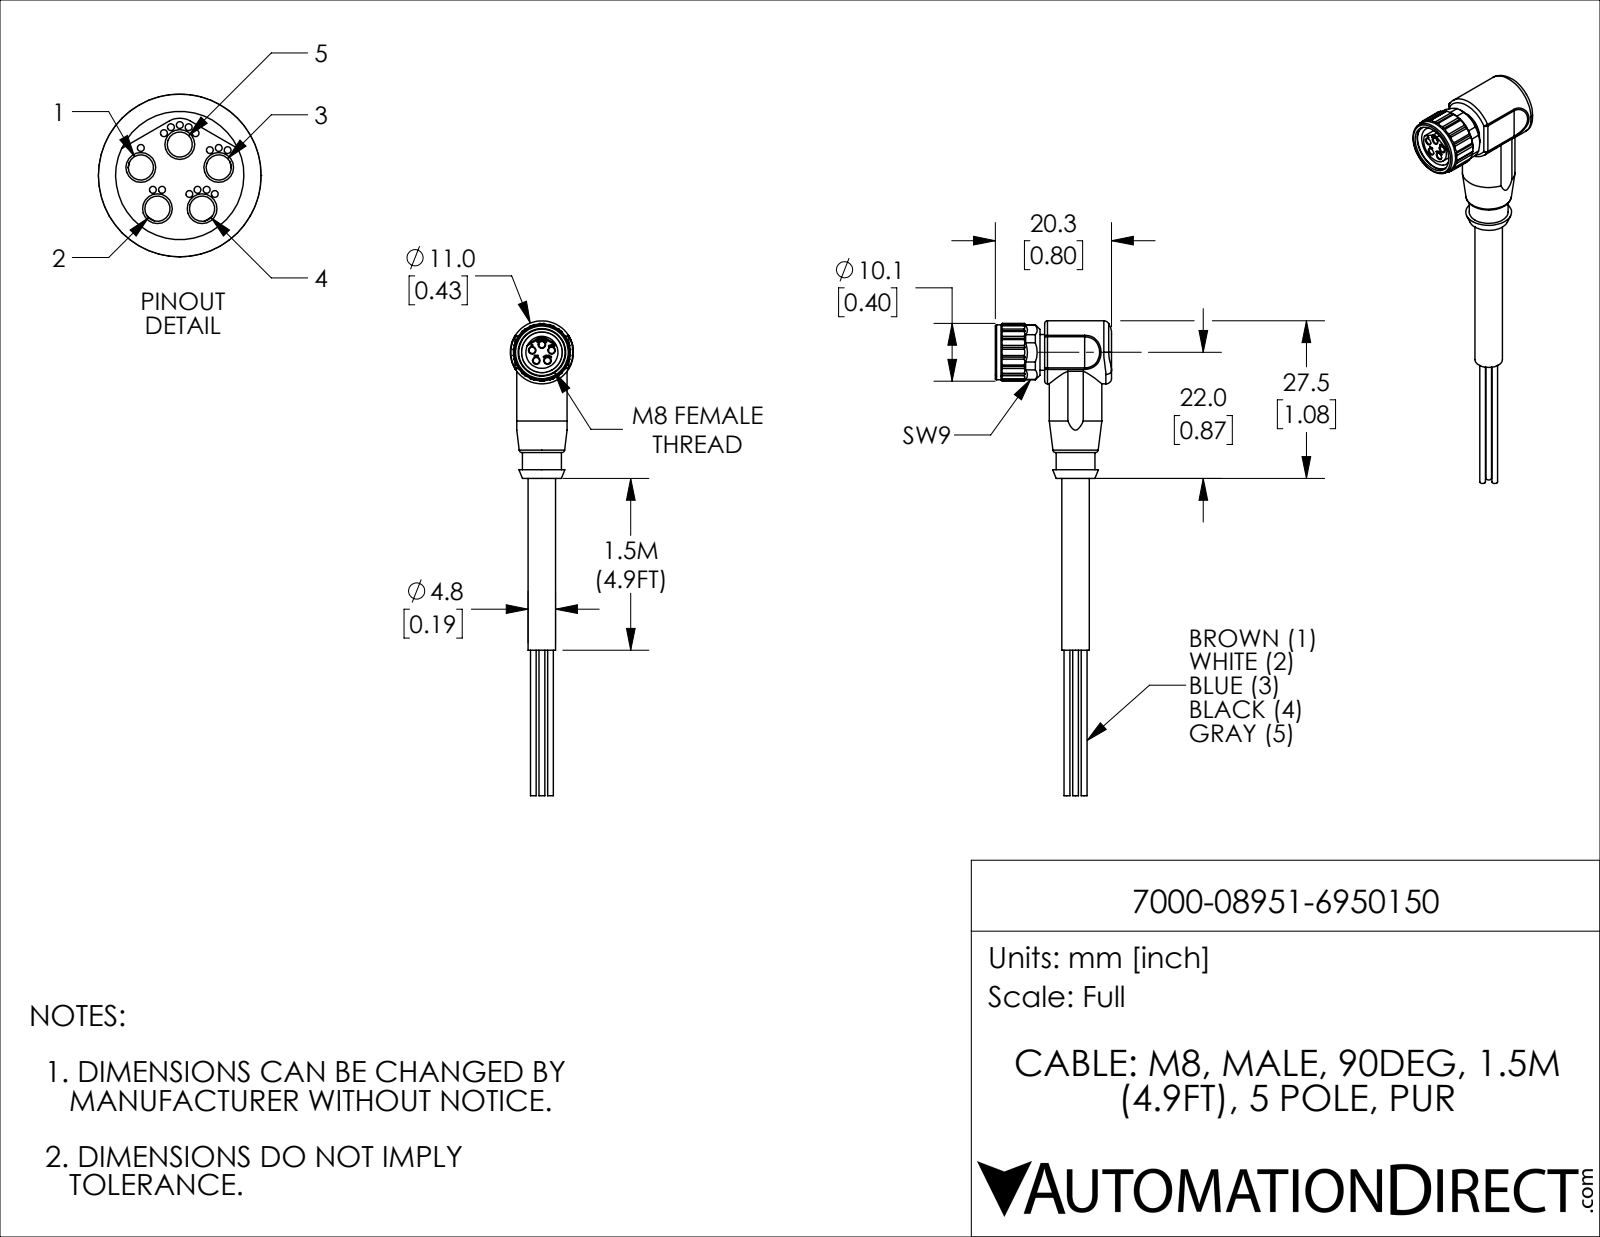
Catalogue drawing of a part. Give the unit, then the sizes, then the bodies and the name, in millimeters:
Units: millimetres
Overall size (bounding box): 82.9 × 20.3 × 11
Round holes (diameter × count): ⌀0.3 ×15, ⌀1.1 ×5, ⌀6.4 ×1, ⌀7.1 ×1, ⌀8.3 ×1
Round bosses / shafts (diameter × count): ⌀1 ×5, ⌀11 ×1, ⌀9.6 ×1, ⌀9.2 ×1, ⌀6.8 ×1, ⌀6.2 ×1, ⌀5.6 ×1, ⌀4.8 ×1
Partial cylindrical surfaces — rounded edges, fillets, slot ends (radius × count): R2 ×18, R0.5 ×8, R0.8 ×6, R0.8 ×4, R0.2 ×2, R3.5 ×2, R5 ×2, R0.6 ×1
Main face-to-face distances: 9.1, 11.7, 9.4, 8.8, 9.1, 0.8, 12.5, 9, 19.6, 7.8
Hole centre spacings: 0.8, 0.4, 2, 0.8, 1.1, 1.8, 1.9, 2.5
Volume: 3 100 mm³ · Surface area: 2 527 mm²
Bodies: 1 solid, 341 faces (135 planar, 152 cylindrical, 54 other)
Part name (STEP PRODUCT): 7000-08951-6950150
STEP written by: SolidWorks 2019 (CONFIG_CONTROL_DESIGN)
